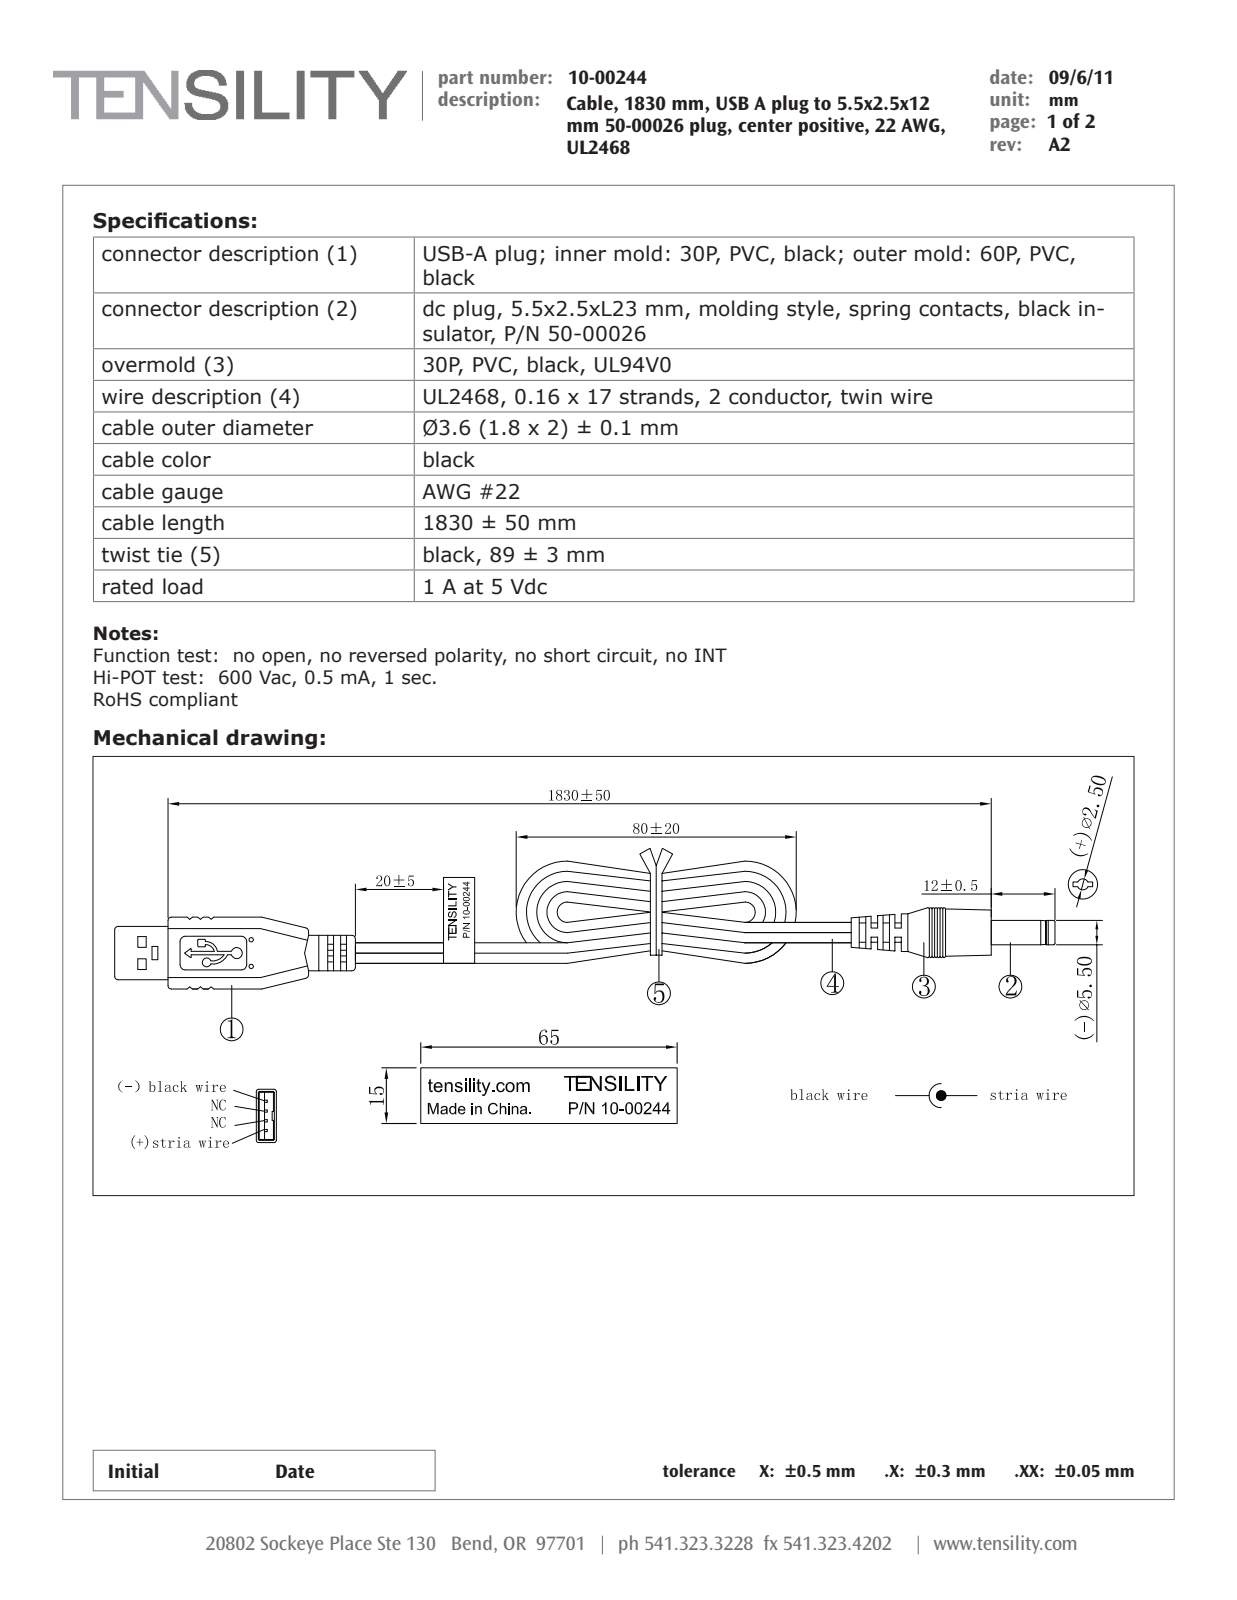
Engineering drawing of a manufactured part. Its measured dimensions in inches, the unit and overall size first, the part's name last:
Units: inches
Overall size (bounding box): 8.939 × 1.522 × 0.366
Round holes (diameter × count): ⌀0.033 ×2, ⌀0.189 ×1, ⌀0.217 ×1
Round bosses / shafts (diameter × count): ⌀0.075 ×2, ⌀0.366 ×1, ⌀0.344 ×1, ⌀0.315 ×1, ⌀0.286 ×1, ⌀0.217 ×1, ⌀0.209 ×1, ⌀0.157 ×1
Partial cylindrical surfaces — rounded edges, fillets, slot ends (radius × count): R0.004 ×26, R0.008 ×18, R0.006 ×8, R0.02 ×8, R0.03 ×8, R0.012 ×6, R0.025 ×4, R0.051 ×4
Main face-to-face distances: 0.077, 0.02, 0.073, 0.071, 0.079, 0.254, 0.092, 0.152, 0.081, 0.177
Hole centre spacings: 0.035, 0.07
Volume: 0.46 in³ · Surface area: 20.89 in²
Bodies: 59 solids, 1131 faces (551 planar, 258 cylindrical, 322 other)
Part name (STEP PRODUCT): 50-00425; 24-00023; 50-00026 shell; 24-00043 (+8 more)
STEP written by: SolidWorks 2015 (AUTOMOTIVE_DESIGN)
